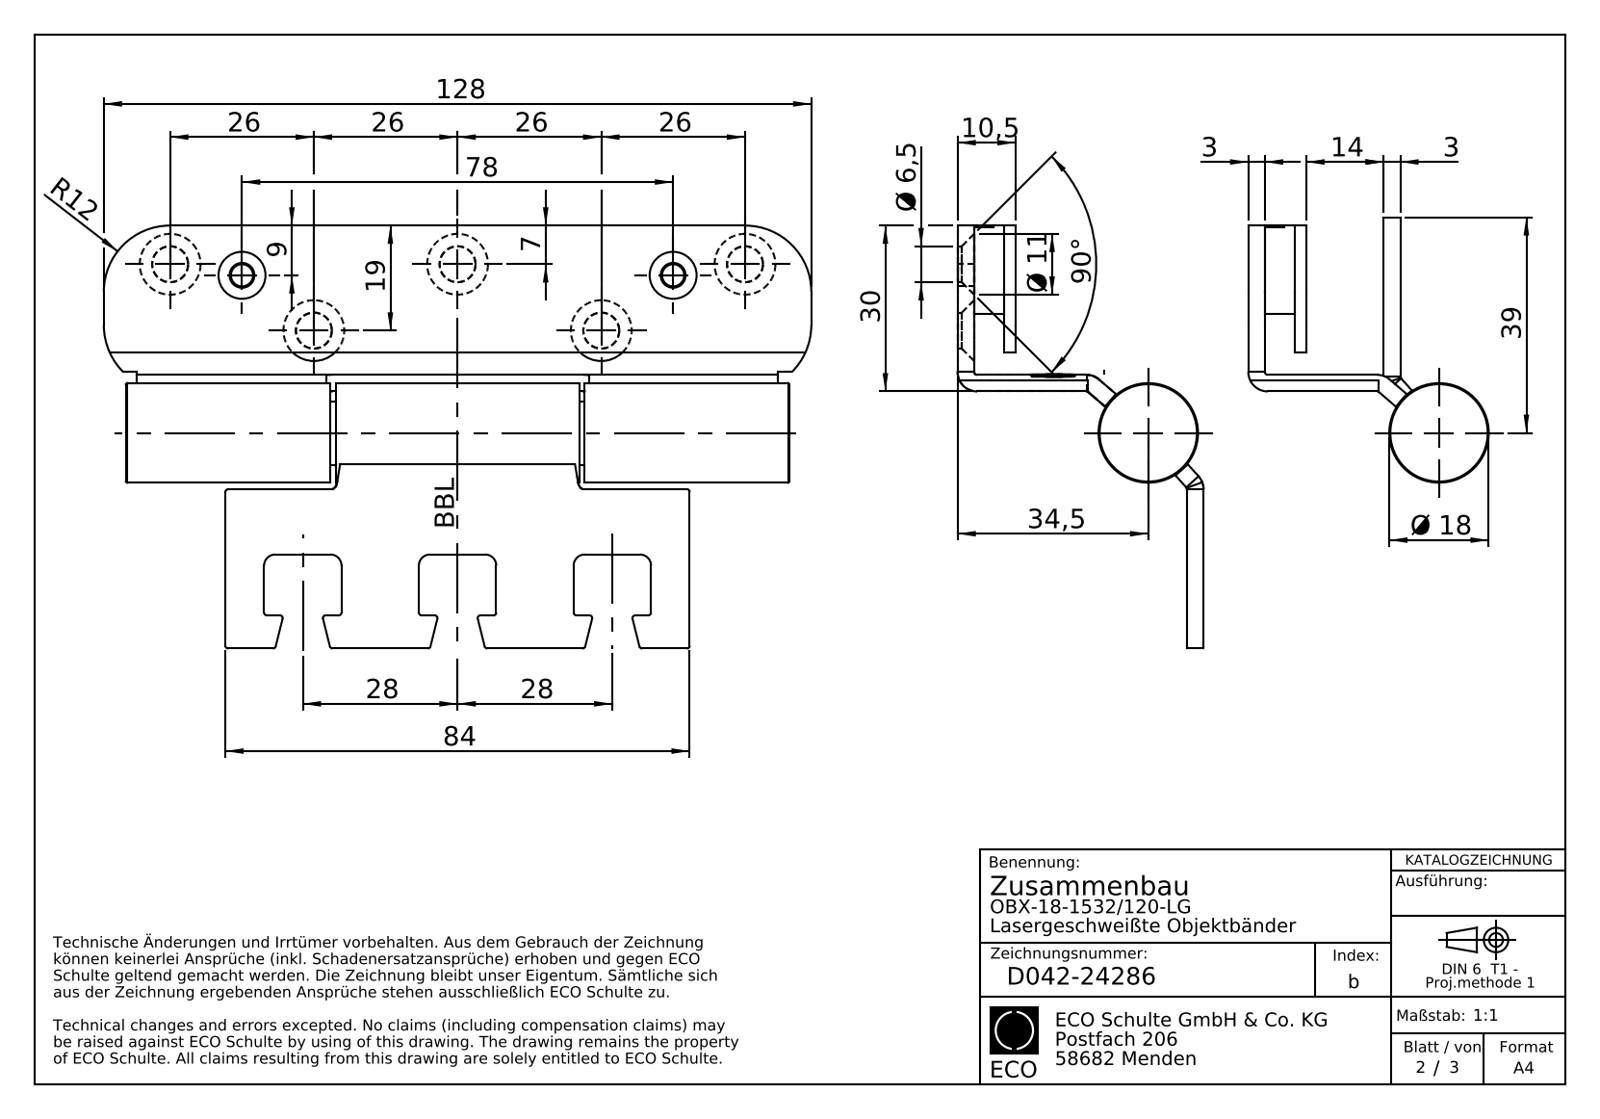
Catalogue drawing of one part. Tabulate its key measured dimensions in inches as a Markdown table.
| quantity | value |
| --- | --- |
| part name | D043-24250; D044-14308; D046-14312; D046-26581 (+6 more) |
| STEP written by | SolidWorks 2020 (CONFIG_CONTROL_DESIGN) |
| units | inches |
| bodies | 13 solids, 569 faces (301 planar, 163 cylindrical, 105 other) |
| overall size | 5.039 × 1.89 × 1.713 |
| volume | 3.97 in³ |
| surface area | 71.35 in² |
| round holes (diameter × count) | 0.256 × 5, 0.079 × 2, 0.157 × 2, 0.197 × 2, 0.02 × 1, 0.177 × 1, 0.311 × 1 |
| round bosses / shafts (diameter × count) | 0.709 × 1, 0.472 × 1, 0.465 × 1, 0.453 × 1, 0.303 × 1, 0.157 × 1, 0.065 × 1 |
| partial cylindrical surfaces (radius × count) | 0.02 × 25, 0.01 × 6, 0.079 × 6, 0.472 × 4, 0.138 × 3, 0.027 × 2, 0.039 × 2, 0.083 × 2 |
| main face-to-face distances | 0.118, 0.079, 0.965, 0.217, 0.335, 0.551, 0.63, 0.295, 0.413, 0.157 |
| hole center spacings | 1.128, 2.047, 0.518, 0.646, 1.537, 2.589, 3.107, 3.583 |
